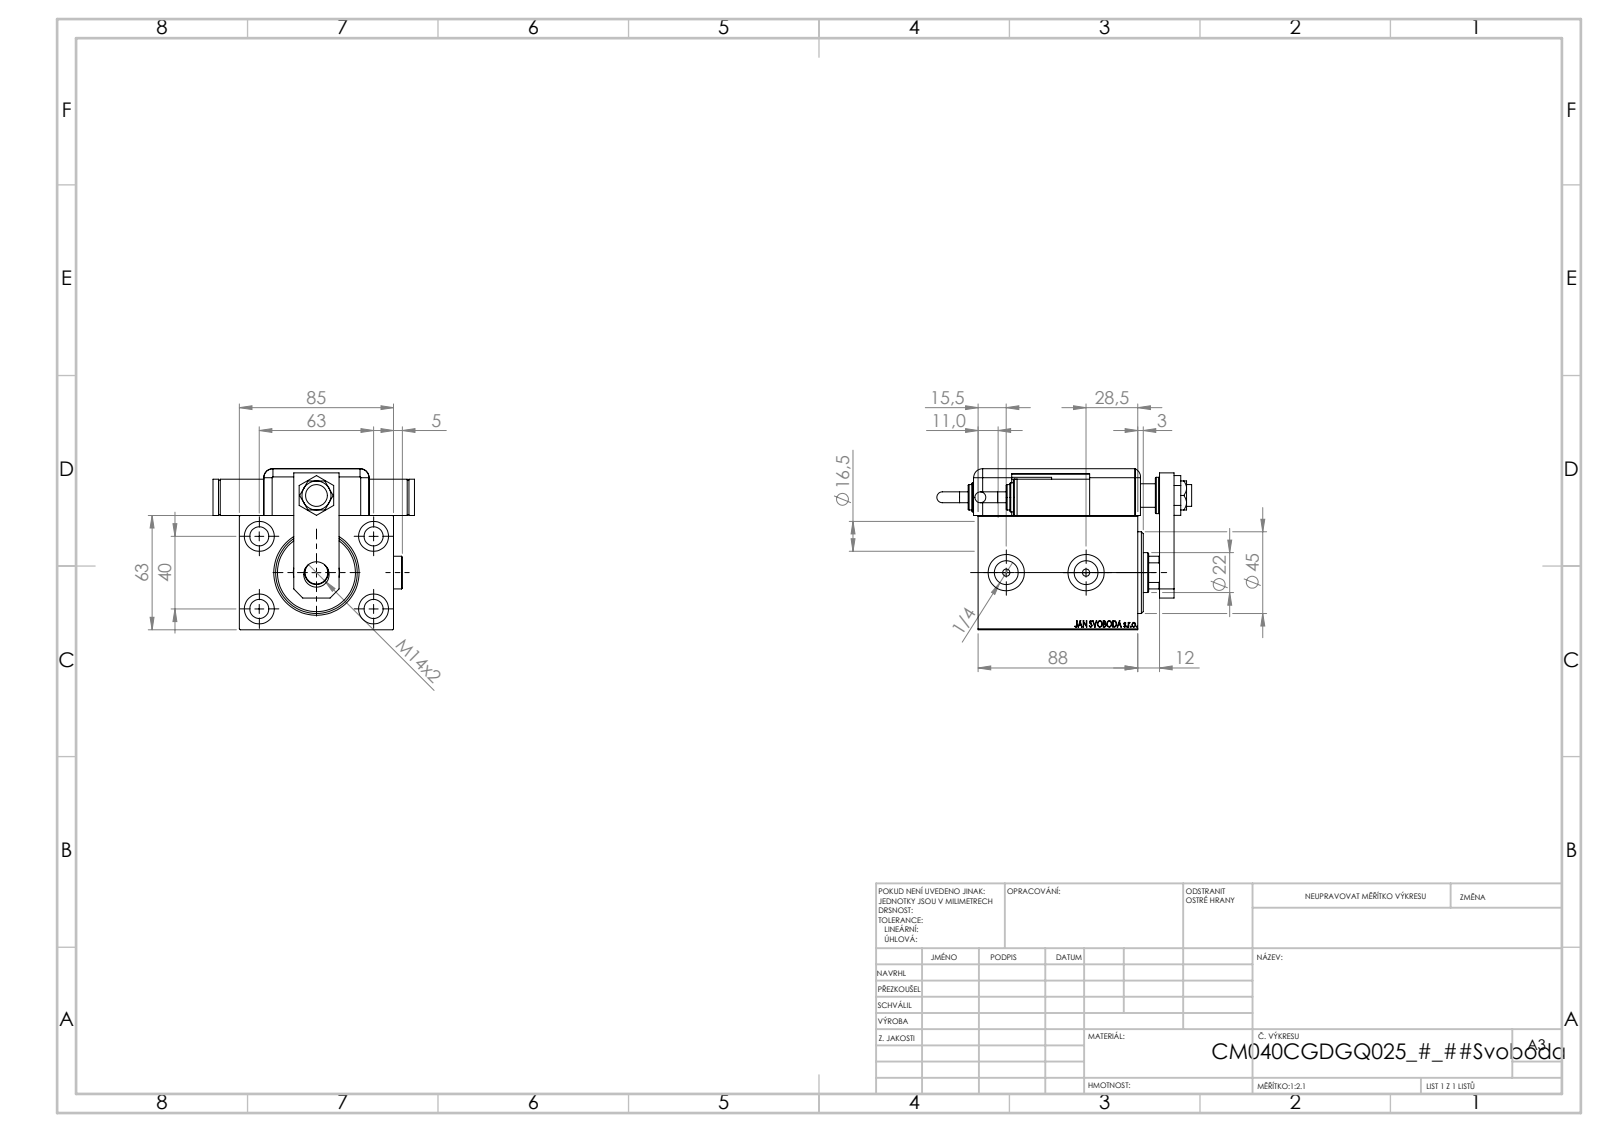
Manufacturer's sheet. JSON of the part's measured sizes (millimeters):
{"part_name": "V450CM_VC_B; TYC; ZARAZKA_Q; V450CM_C_Body (+7 more)", "step_written_by": "SolidWorks 2019 (CONFIG_CONTROL_DESIGN)", "units": "millimeters", "bodies": {"solids": 15, "faces": 1300, "planar": 648, "cylindrical": 131, "other": 521}, "overall_size": [140.46, 111, 88.8], "volume_mm3": 540819, "surface_area_mm2": 130727, "round_holes": [[4, 4], [10.5, 4], [16.5, 4], [8, 2], [13.16, 2], [14, 2], [20, 2], [12, 1], [12.5, 1], [13, 1], [22, 1], [25.5, 1]], "round_bosses_or_shafts": [[20, 3], [18, 2], [16, 2], [14, 2], [6, 2]], "partial_cylinders_radius": [[5, 9], [10, 1], [10.5, 1]], "face_to_face_distances": [3, 63, 13.5, 85, 12, 83, 10.5, 20, 88, 1.5], "hole_center_spacings": [37.31, 36.79, 37.86, 38.71, 40, 63, 69.99, 74.63]}
